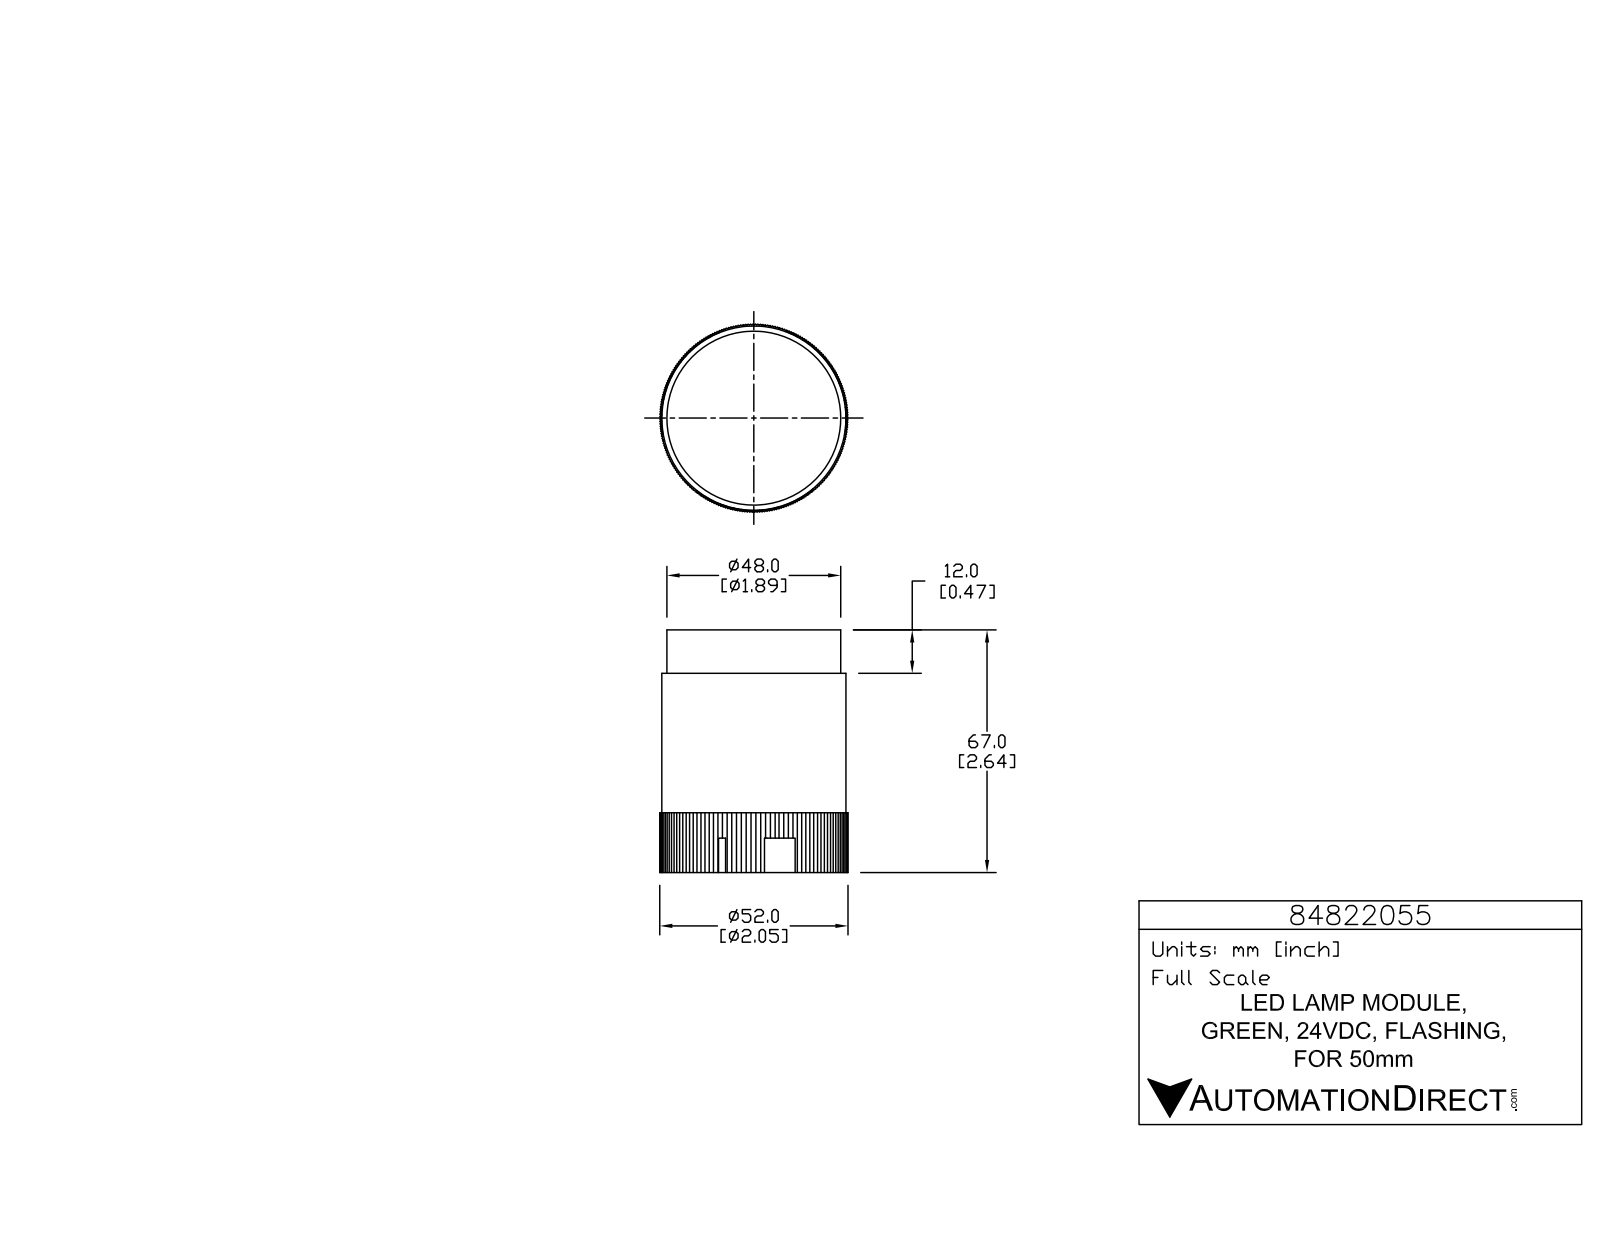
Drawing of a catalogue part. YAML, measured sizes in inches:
part_name: "84822055"
step_written_by: "SolidWorks 2015 (AUTOMOTIVE_DESIGN)"
units: inches
bodies: {solids: 1, faces: 1265, planar: 1020, cylindrical: 245, other: 0}
overall_size: [2.638, 2.047, 2.047]
volume: 6.873
surface_area: 27.62
round_holes:
  - {diameter: 0.039, count: 3}
  - {diameter: 1.898, count: 1}
round_bosses_or_shafts:
  - {diameter: 0.226, count: 3}
  - {diameter: 0.056, count: 3}
  - {diameter: 2.002, count: 1}
  - {diameter: 1.89, count: 1}
partial_cylinders:
  - {radius: 0.008, count: 6}
  - {radius: 0.008, count: 6}
  - {radius: 0.008, count: 6}
  - {radius: 0.131, count: 6}
  - {radius: 0.004, count: 3}
  - {radius: 0.005, count: 3}
  - {radius: 0.008, count: 3}
  - {radius: 0.008, count: 3}
face_to_face_distances: [2.165, 1.428, 1.429, 1.429, 0.472, 2.638, 1.428, 1.428, 1.693, 1.988]
